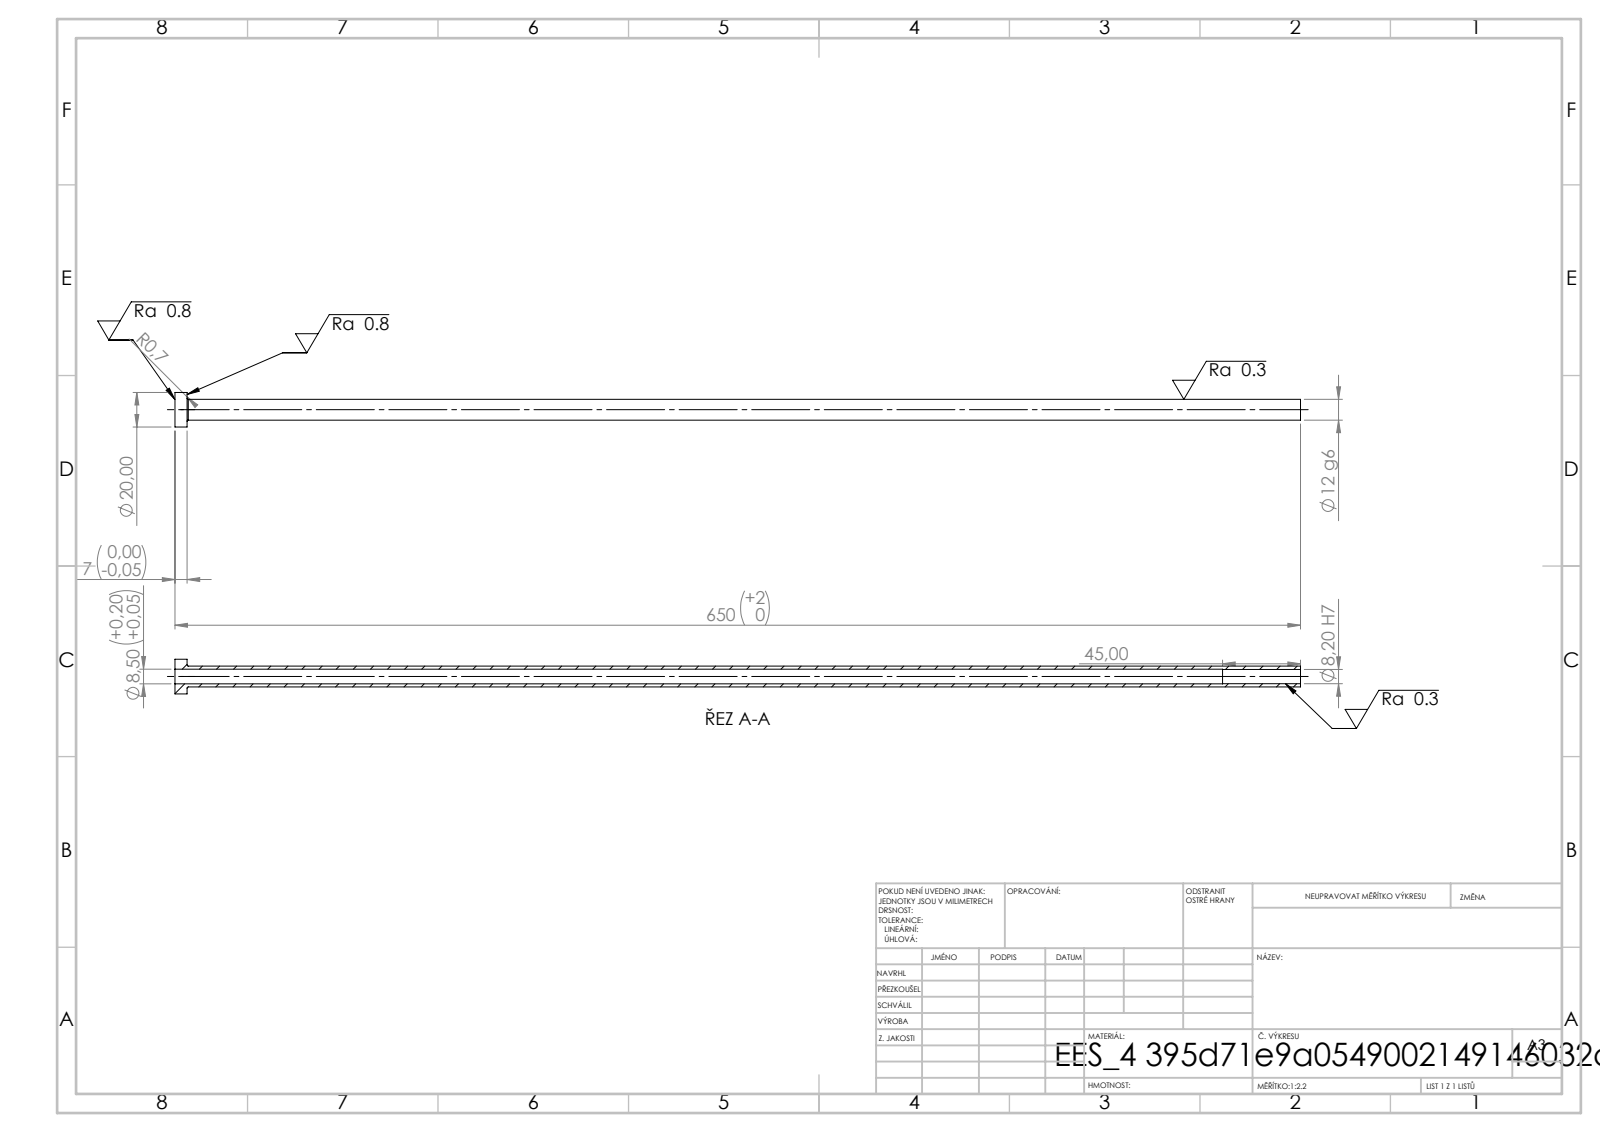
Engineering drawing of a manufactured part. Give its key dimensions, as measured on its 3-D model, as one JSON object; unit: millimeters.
{"step_written_by": "SolidWorks 2019 (CONFIG_CONTROL_DESIGN)", "units": "millimeters", "bodies": {"solids": 1, "faces": 14, "planar": 4, "cylindrical": 8, "other": 2}, "overall_size": [650, 20, 20], "volume_mm3": 38218, "surface_area_mm2": 42507, "round_holes": [[8.2, 1], [8.5, 1]], "round_bosses_or_shafts": [[20, 1], [12, 1]], "face_to_face_distances": [7, 650, 643, 605, 598, 45]}
